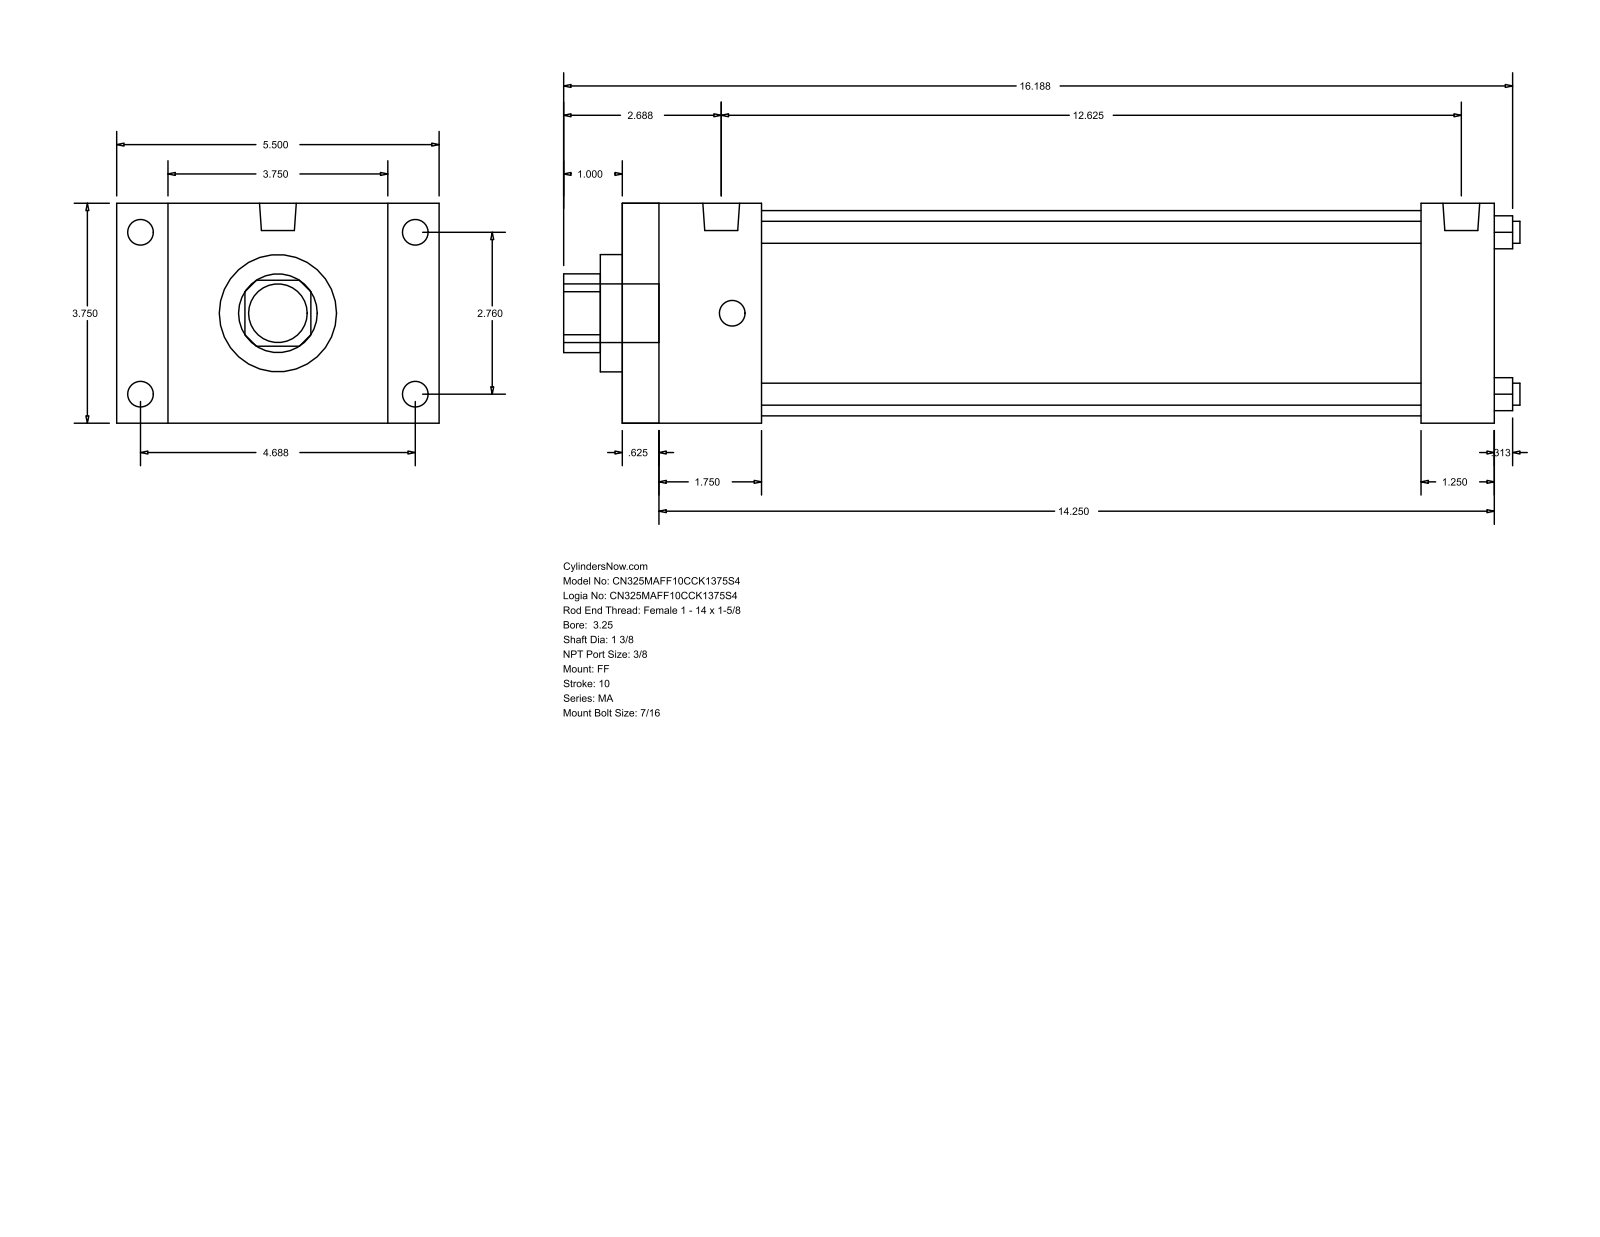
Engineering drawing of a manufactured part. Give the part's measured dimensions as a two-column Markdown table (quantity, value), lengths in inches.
| quantity | value |
| --- | --- |
| part name | MA_FF__0325_1.375 |
| STEP written by | GSSL Pune (CONFIG_CONTROL_DESIGN) |
| units | inches |
| bodies | 0 solids, 92 faces (64 planar, 28 cylindrical, 0 other) |
| overall size | 16.313 × 5.5 × 3.75 |
| round holes (diameter × count) | 0.375 × 4, 1.375 × 1, 2 × 1, 3.5 × 1 |
| round bosses / shafts (diameter × count) | 0.437 × 8, 0.627 × 2, 1 × 1 |
| partial cylindrical surfaces (radius × count) | 0.672 × 1 |
| main face-to-face distances | 3.75, 14.875, 0.625, 14.25, 0.875, 4.625, 2.375, 13.625, 1.75, 13 |
| hole center spacings | 1.952, 2.76, 3.903 |
